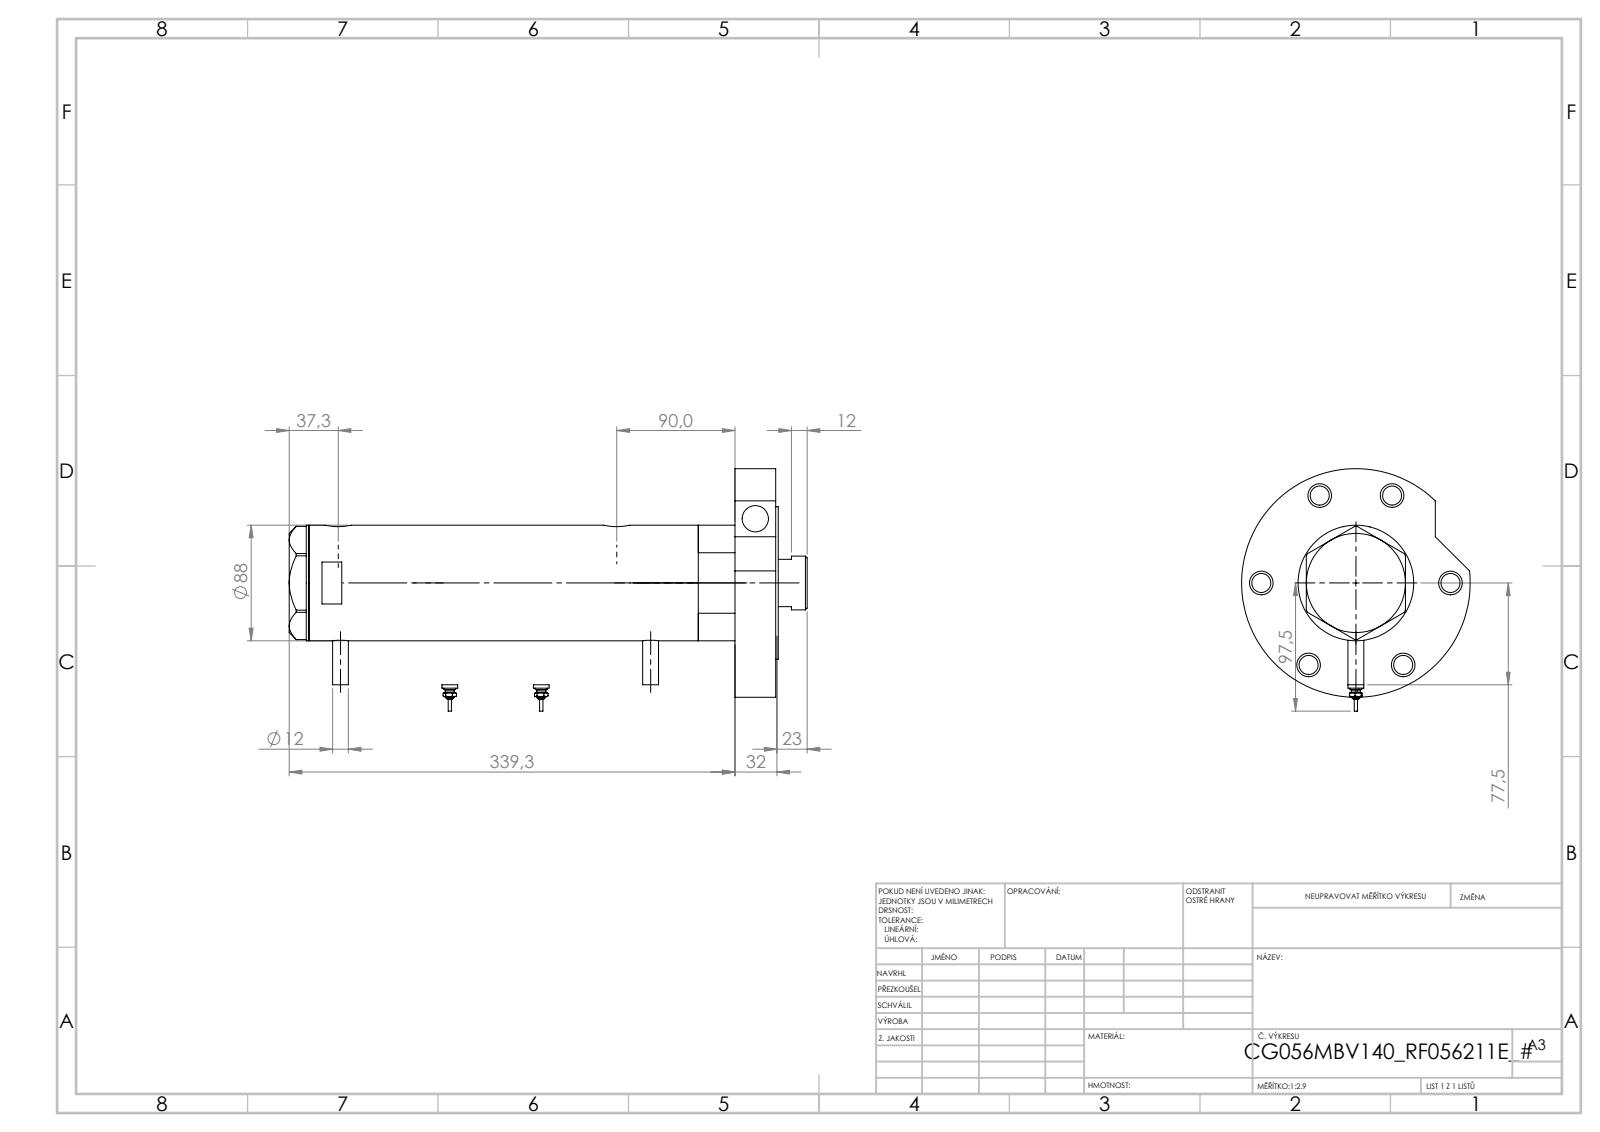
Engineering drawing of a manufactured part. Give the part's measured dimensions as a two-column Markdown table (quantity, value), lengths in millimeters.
| quantity | value |
| --- | --- |
| part name | Switch; V270CG_VC; V270CG_MIDDLE; V270CG_BACK (+2 more) |
| STEP written by | SolidWorks 2019 (CONFIG_CONTROL_DESIGN) |
| units | millimeters |
| bodies | 7 solids, 257 faces (91 planar, 102 cylindrical, 64 other) |
| overall size | 394.3 × 184.5 × 174 |
| volume | 2 572 000 mm³ |
| surface area | 361 131 mm² |
| round holes (diameter × count) | 14.5 × 7, 18 × 6, 20 × 3, 12.5 × 2, 13.16 × 2, 42 × 1, 43.5 × 1, 56 × 1, 60 × 1, 75 × 1, 80 × 1 |
| round bosses / shafts (diameter × count) | 12 × 4, 9 × 2, 7 × 2, 4.5 × 2, 2.5 × 2, 174 × 1, 116 × 1, 88 × 1 |
| main face-to-face distances | 31, 2, 357.3, 324.3, 355.3, 33, 234.4, 89.9, 120.9, 122.9 |
| hole center spacings | 72, 80, 119.73, 124.71, 129.15, 143.69, 1.7, 25.8 |
